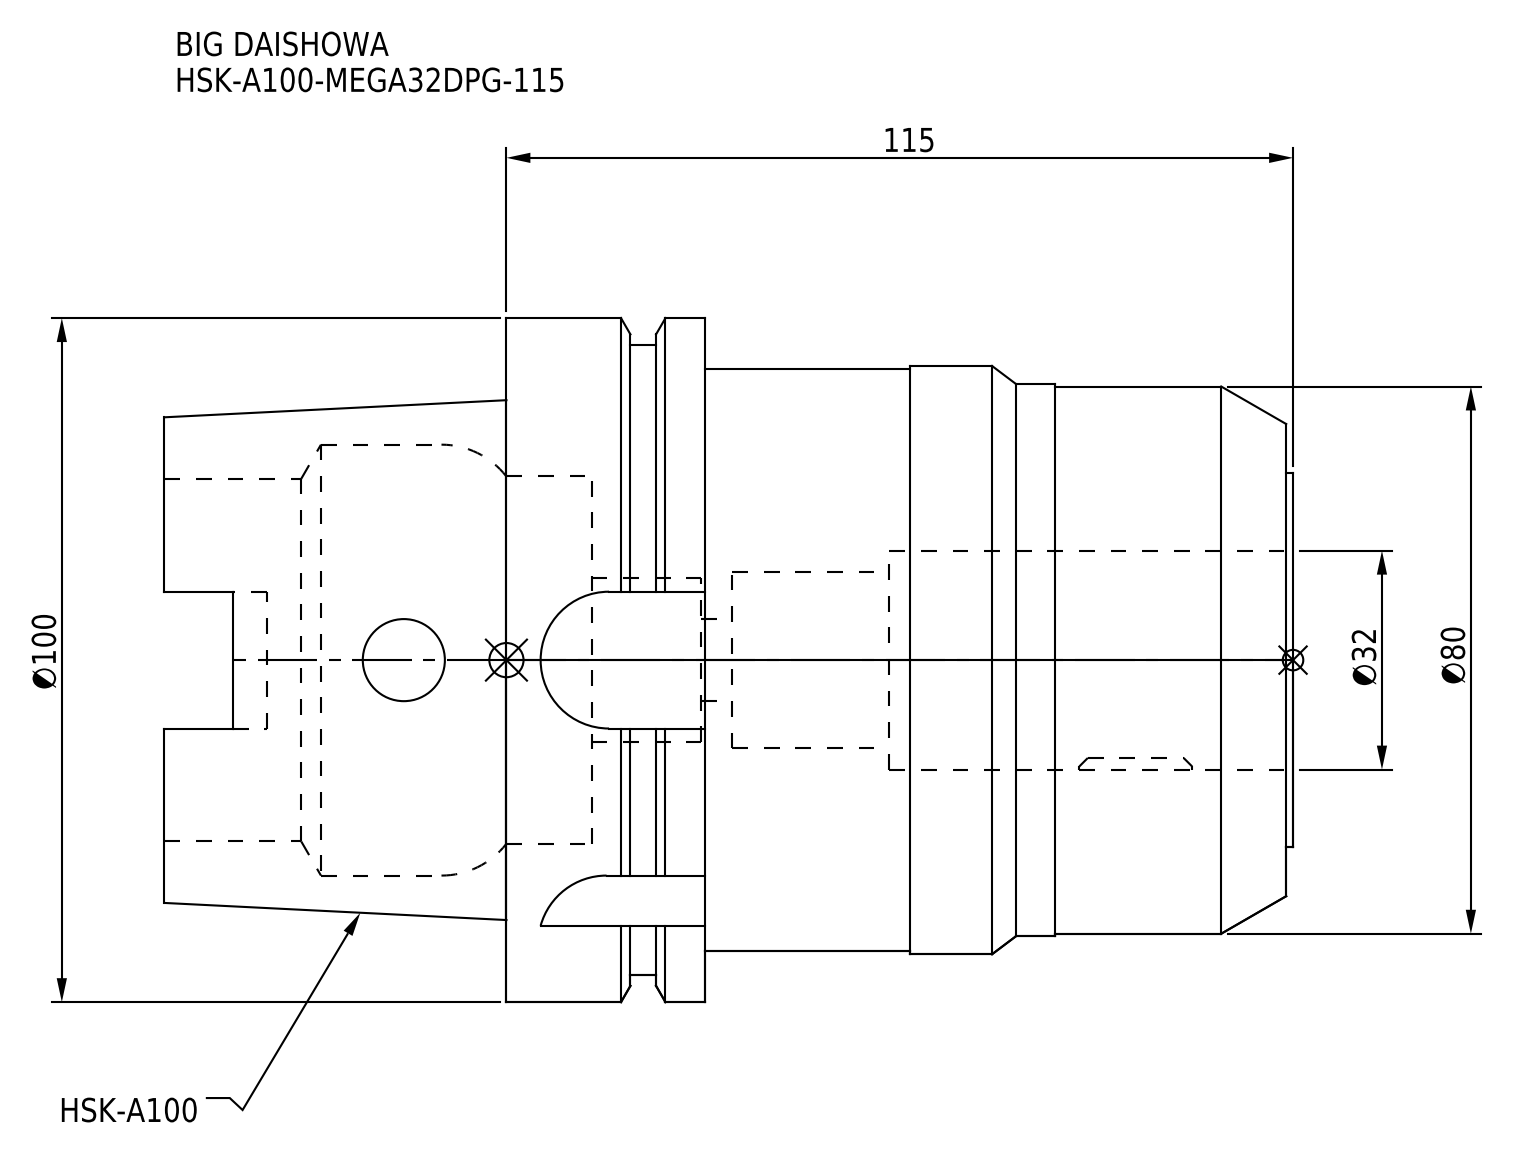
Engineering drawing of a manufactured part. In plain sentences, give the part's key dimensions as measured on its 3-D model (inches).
The part is named "HSK-A100-MEGA32DPG-115". Its 3-D file was written by "CREO PARAMETRIC BY PTC INC, 2016380 (AUTOMOTIVE_DESIGN)". It is 1 solid with 101 faces: 37 planar, 46 cylindrical and 18 other. Overall it measures 6.496 by 3.937 by 3.937 inches. Its volume is 39.53 cubic inches and its surface area 122 square inches. Round holes: 2 of diameter 0.472, 1 of diameter 0.945, 1 of diameter 1.016, 1 of diameter 1.26, 1 of diameter 2.087, 1 of diameter 2.118, 1 of diameter 2.48. Round bosses or shafts: 1 of diameter 3.937, 1 of diameter 3.622, 1 of diameter 3.386, 1 of diameter 3.346, 1 of diameter 3.177, 1 of diameter 3.15, 1 of diameter 2.154. Partial cylindrical surfaces (rounded edges, fillets, slot ends): 4 of radius 0.192, 4 of radius 0.394. The main face-to-face distances are 1.142, 0.652, 0.49, 3.386, 4.037, 4.528, 0.039, 3.346, 3.998, 4.488.
